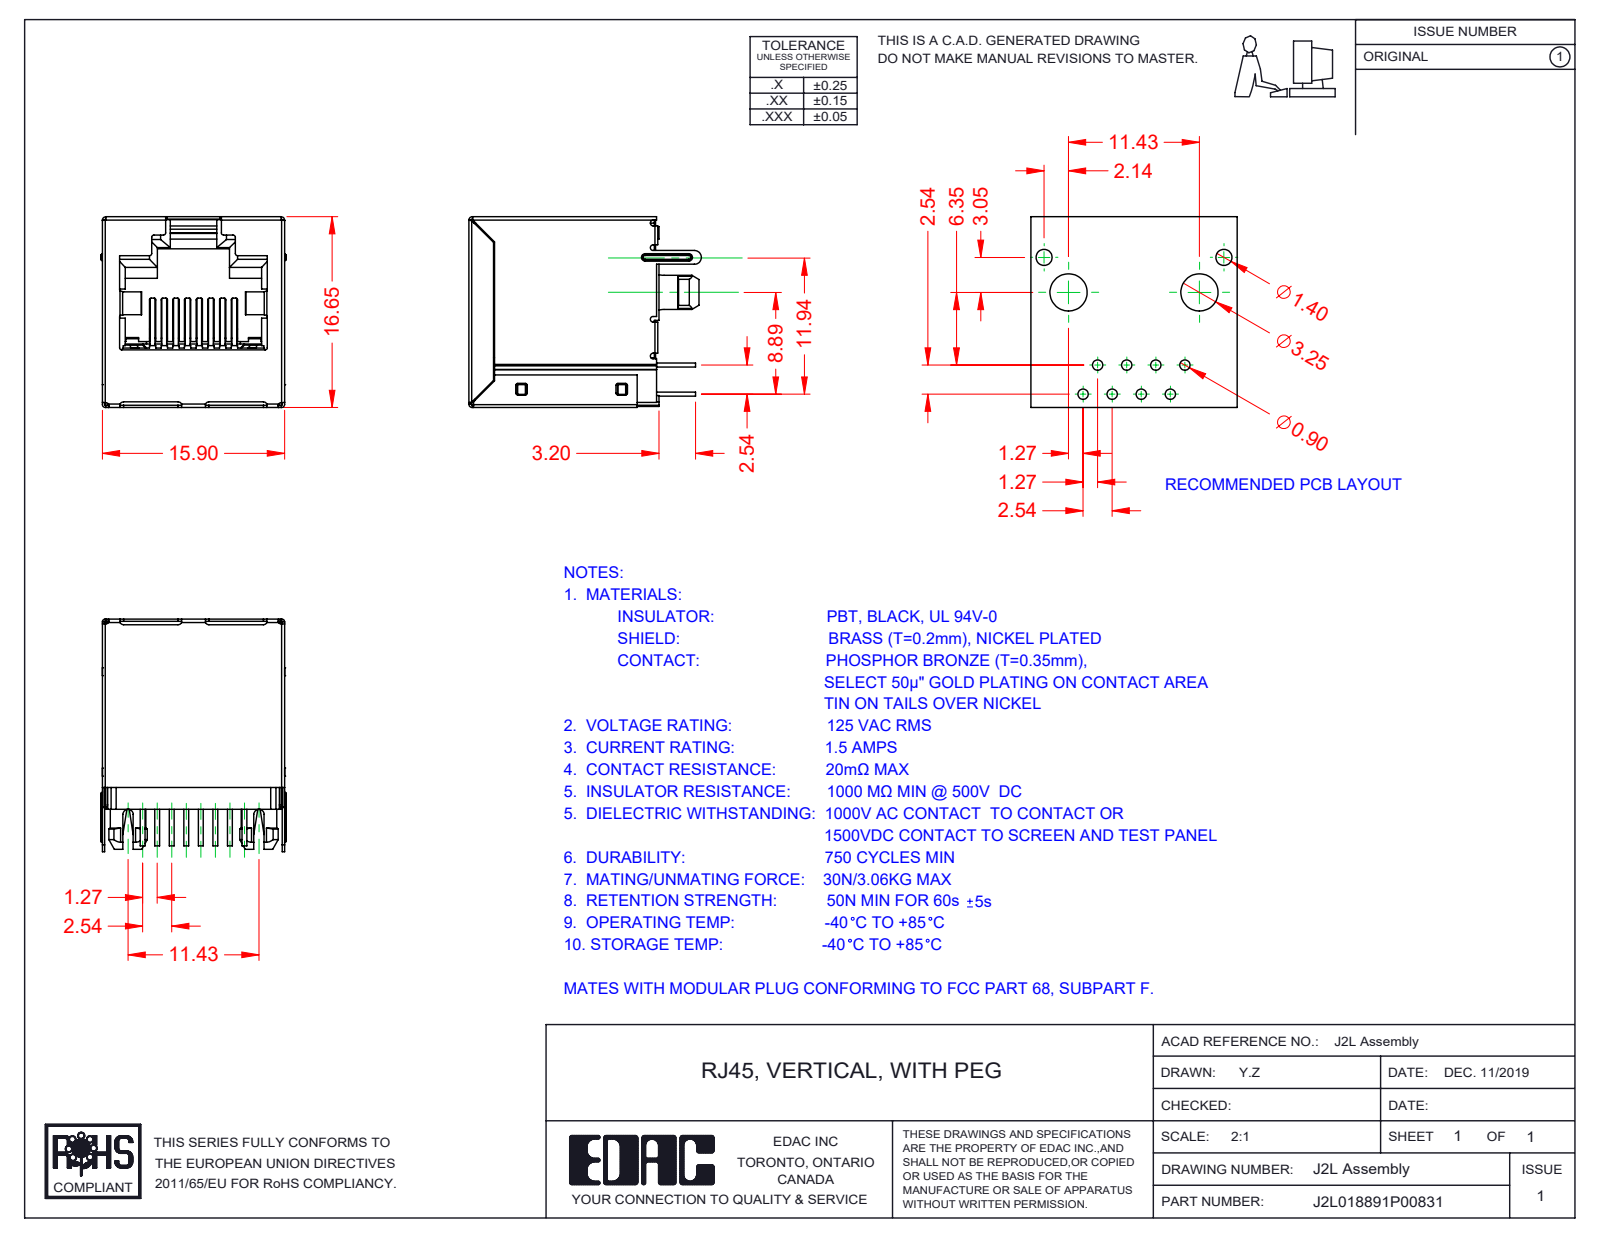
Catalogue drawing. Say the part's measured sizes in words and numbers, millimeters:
The part is named "2L Mylar Tape; 2L Contacts; 2L Shield; RJ2L018891P00831 (+2 more)". Its 3-D file was written by "SolidWorks 2016 (CONFIG_CONTROL_DESIGN)". It is 12 solids with 1131 faces: 784 planar, 284 cylindrical and 63 other. Overall it measures 20.3 by 16.65 by 16.2 millimeters. Its volume is 2 735 cubic millimeters and its surface area 6 843 square millimeters. Round bosses or shafts: 2 of diameter 3.1, 2 of diameter 1.1. Partial cylindrical surfaces (rounded edges, fillets, slot ends): 64 of radius 0.15, 20 of radius 0.25, 16 of radius 0.2, 14 of radius 0.3, 9 of radius 0.35, 8 of radius 0.1, 4 of radius 0.28, 3 of radius 0.5. The main face-to-face distances are 15.45, 15.7, 16.45, 16.2, 16.4, 15.65, 16.3, 16.25, 15.9, 15.5.
